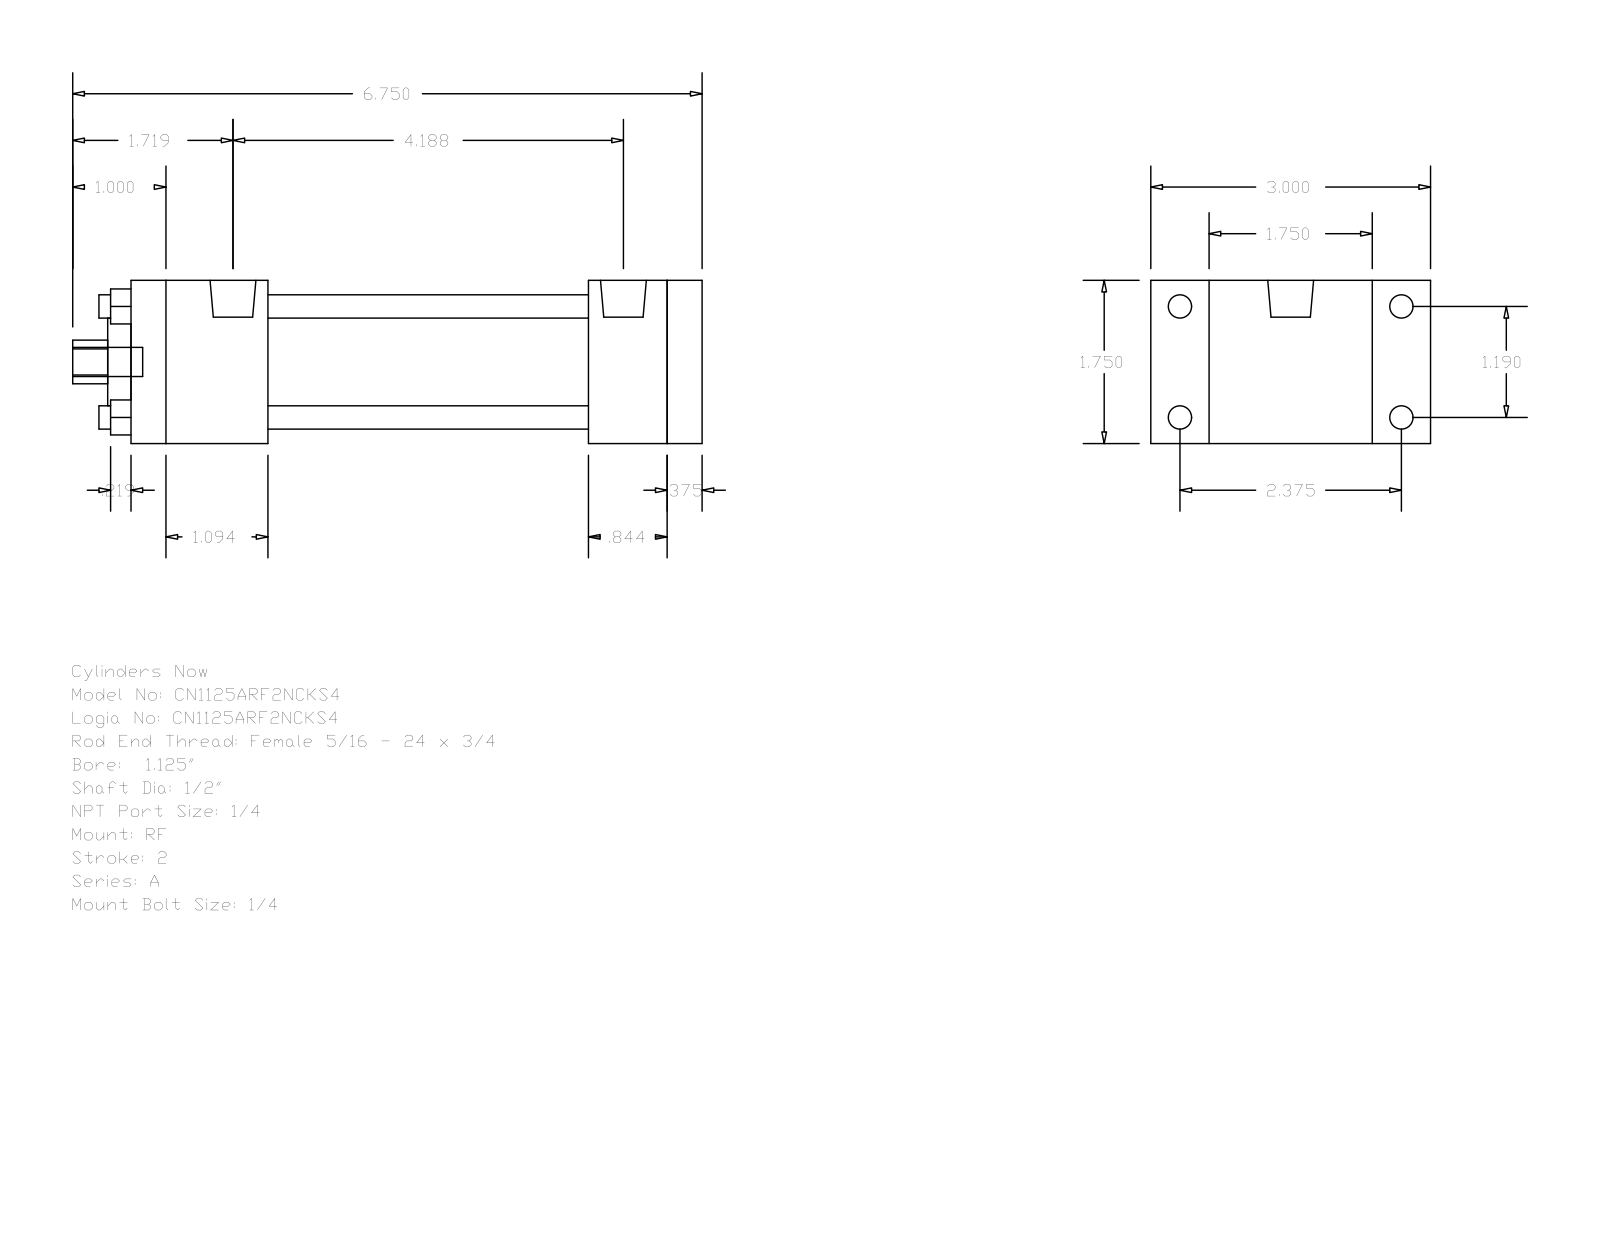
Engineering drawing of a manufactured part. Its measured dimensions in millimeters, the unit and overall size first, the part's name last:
Units: millimetres
Overall size (bounding box): 171.45 × 76.2 × 44.45
Round holes (diameter × count): ⌀6.35 ×4, ⌀12.7 ×1, ⌀23.81 ×1, ⌀31.88 ×1
Round bosses / shafts (diameter × count): ⌀6.35 ×4, ⌀5.56 ×4, ⌀12.49 ×2, ⌀7.94 ×1
Partial cylindrical surfaces — rounded edges, fillets, slot ends (radius × count): R5.94 ×1
Main face-to-face distances: 44.46, 9.52, 146.05, 155.57, 37.3, 124.61, 87.31, 108.75, 118.27, 21.44
Hole centre spacings: 21.37, 30.22, 42.74
Bodies: 0 solids, 92 faces (64 planar, 28 cylindrical, 0 other)
Part name (STEP PRODUCT): A_RF__0112_0.5
STEP written by: GSSL Pune (CONFIG_CONTROL_DESIGN)
